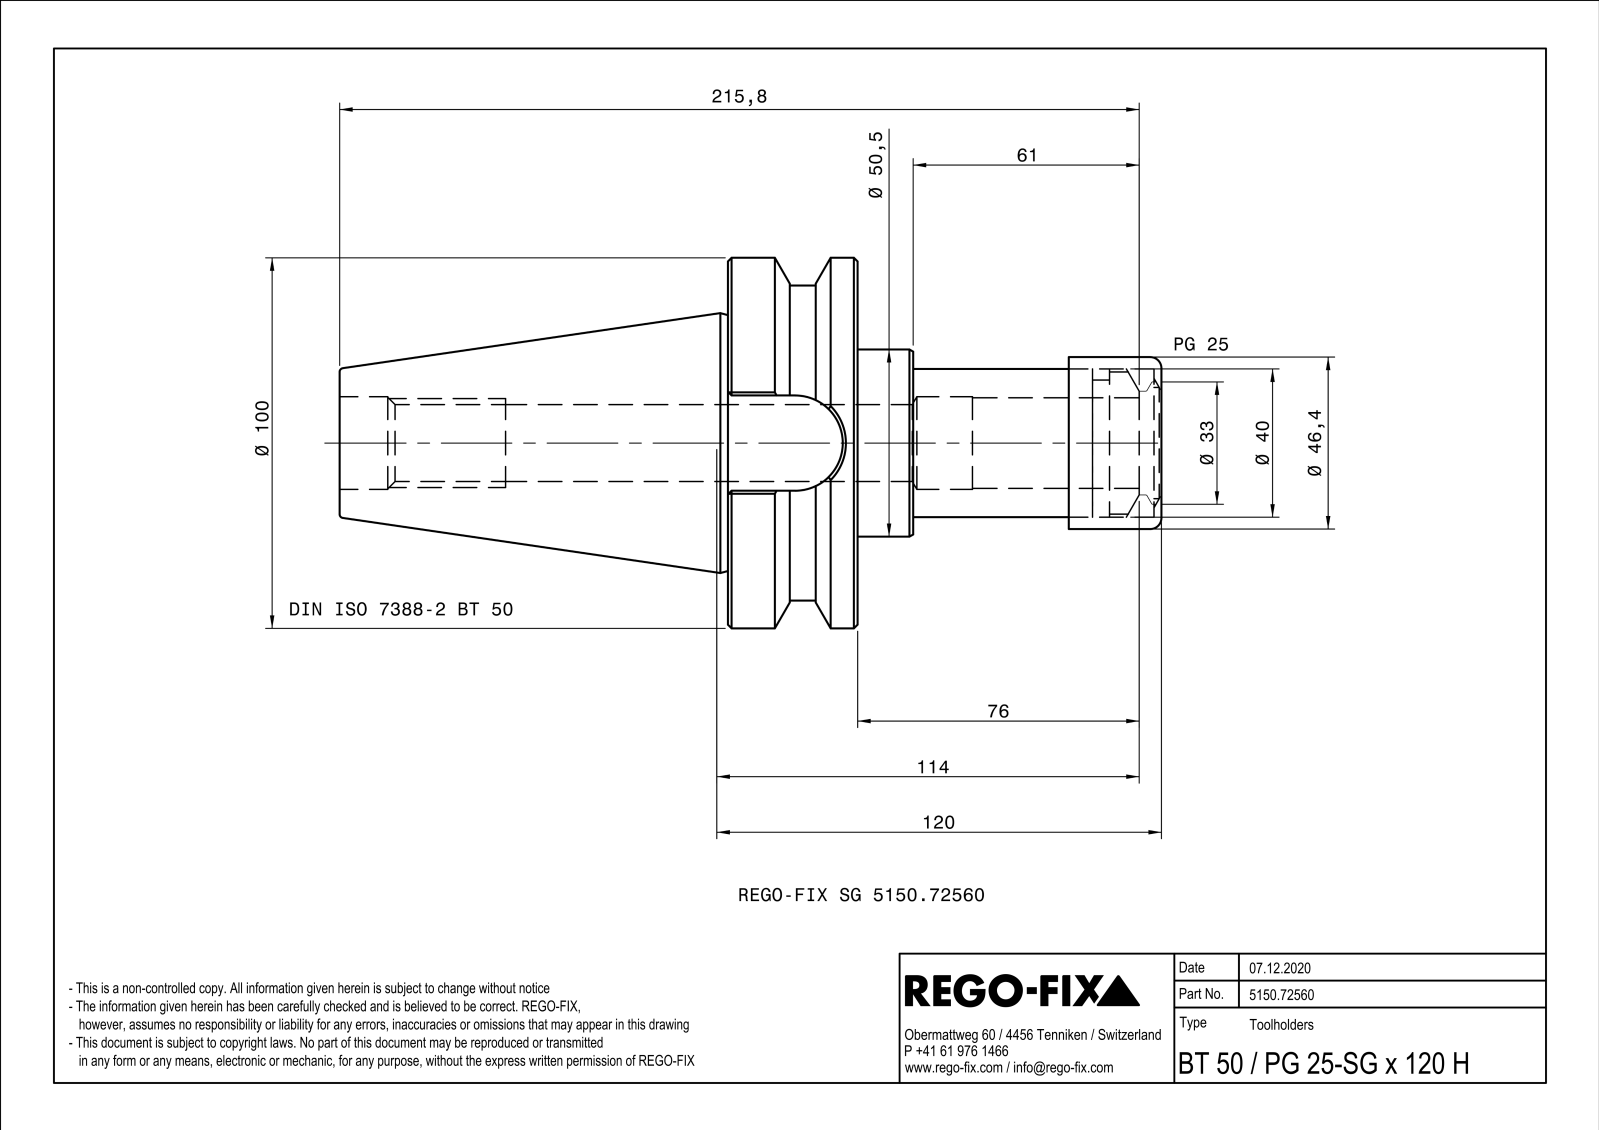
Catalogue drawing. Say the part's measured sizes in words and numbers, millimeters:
The part is named "0013428". Its 3-D file was written by "SIEMENS PLM Software Solid Edge ST10 (AUTOMOTIVE_DESIGN)". It is 1 solid with 101 faces: 35 planar, 24 cylindrical and 42 other. Overall it measures 221.8 by 100 by 100 millimeters. Its volume is 523 988 cubic millimeters and its surface area 76 195 square millimeters. Round holes: 1 of diameter 20.75, 1 of diameter 25, 1 of diameter 30, 1 of diameter 38.38, 1 of diameter 40.05, 1 of diameter 42. Round bosses or shafts: 1 of diameter 100, 1 of diameter 85, 1 of diameter 50.5, 1 of diameter 46.4, 1 of diameter 46, 1 of diameter 40, 1 of diameter 34. Partial cylindrical surfaces (rounded edges, fillets, slot ends): 4 of radius 0.5, 1 of radius 12.85. The main face-to-face distances are 35, 70.7, 139.8, 104.8, 82, 117, 221.8, 67, 15, 50.
